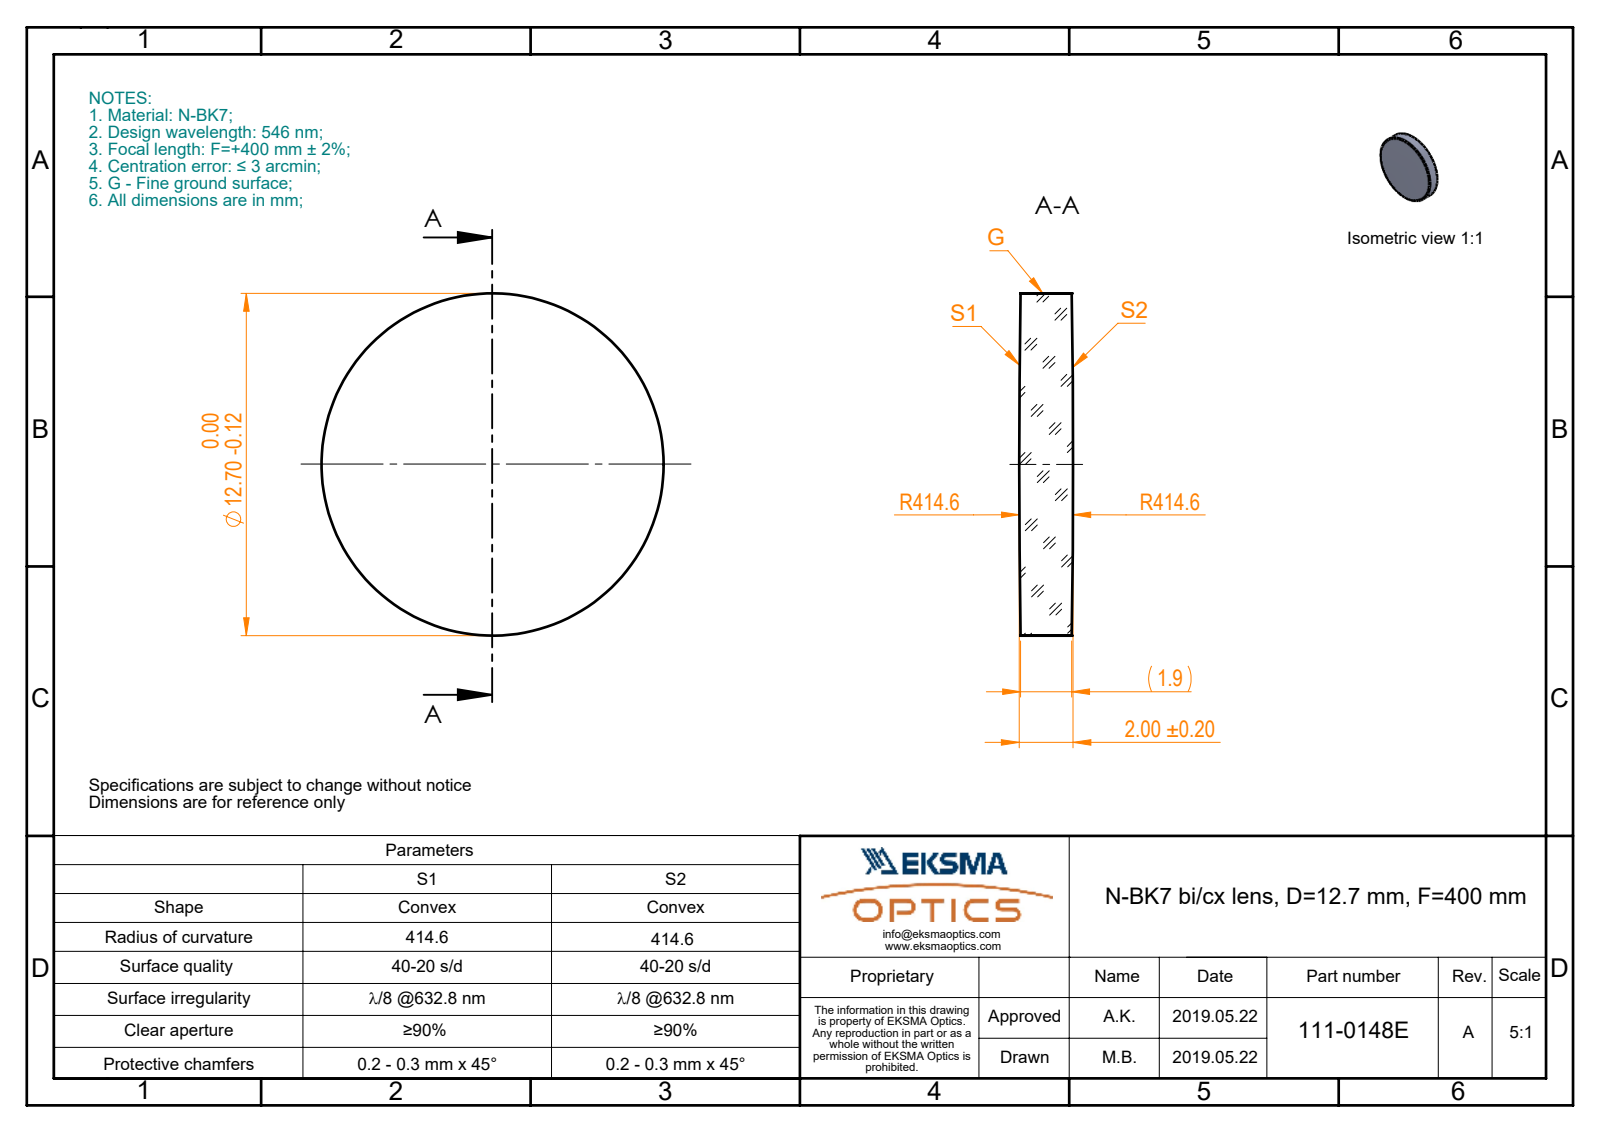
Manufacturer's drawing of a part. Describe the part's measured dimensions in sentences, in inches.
The part is named "111-0148E BK7 bi-cx 12.7 F400". Its 3-D file was written by "SolidWorks 2017 (CONFIG_CONTROL_DESIGN)". It is 1 solid with 6 faces: 0 planar, 2 cylindrical and 4 other. Overall it measures 0.5 by 0.5 by 0.079 inches. Its volume is 0.015 cubic inches and its surface area 0.51 square inches. Round bosses or shafts: 1 of diameter 0.5.
